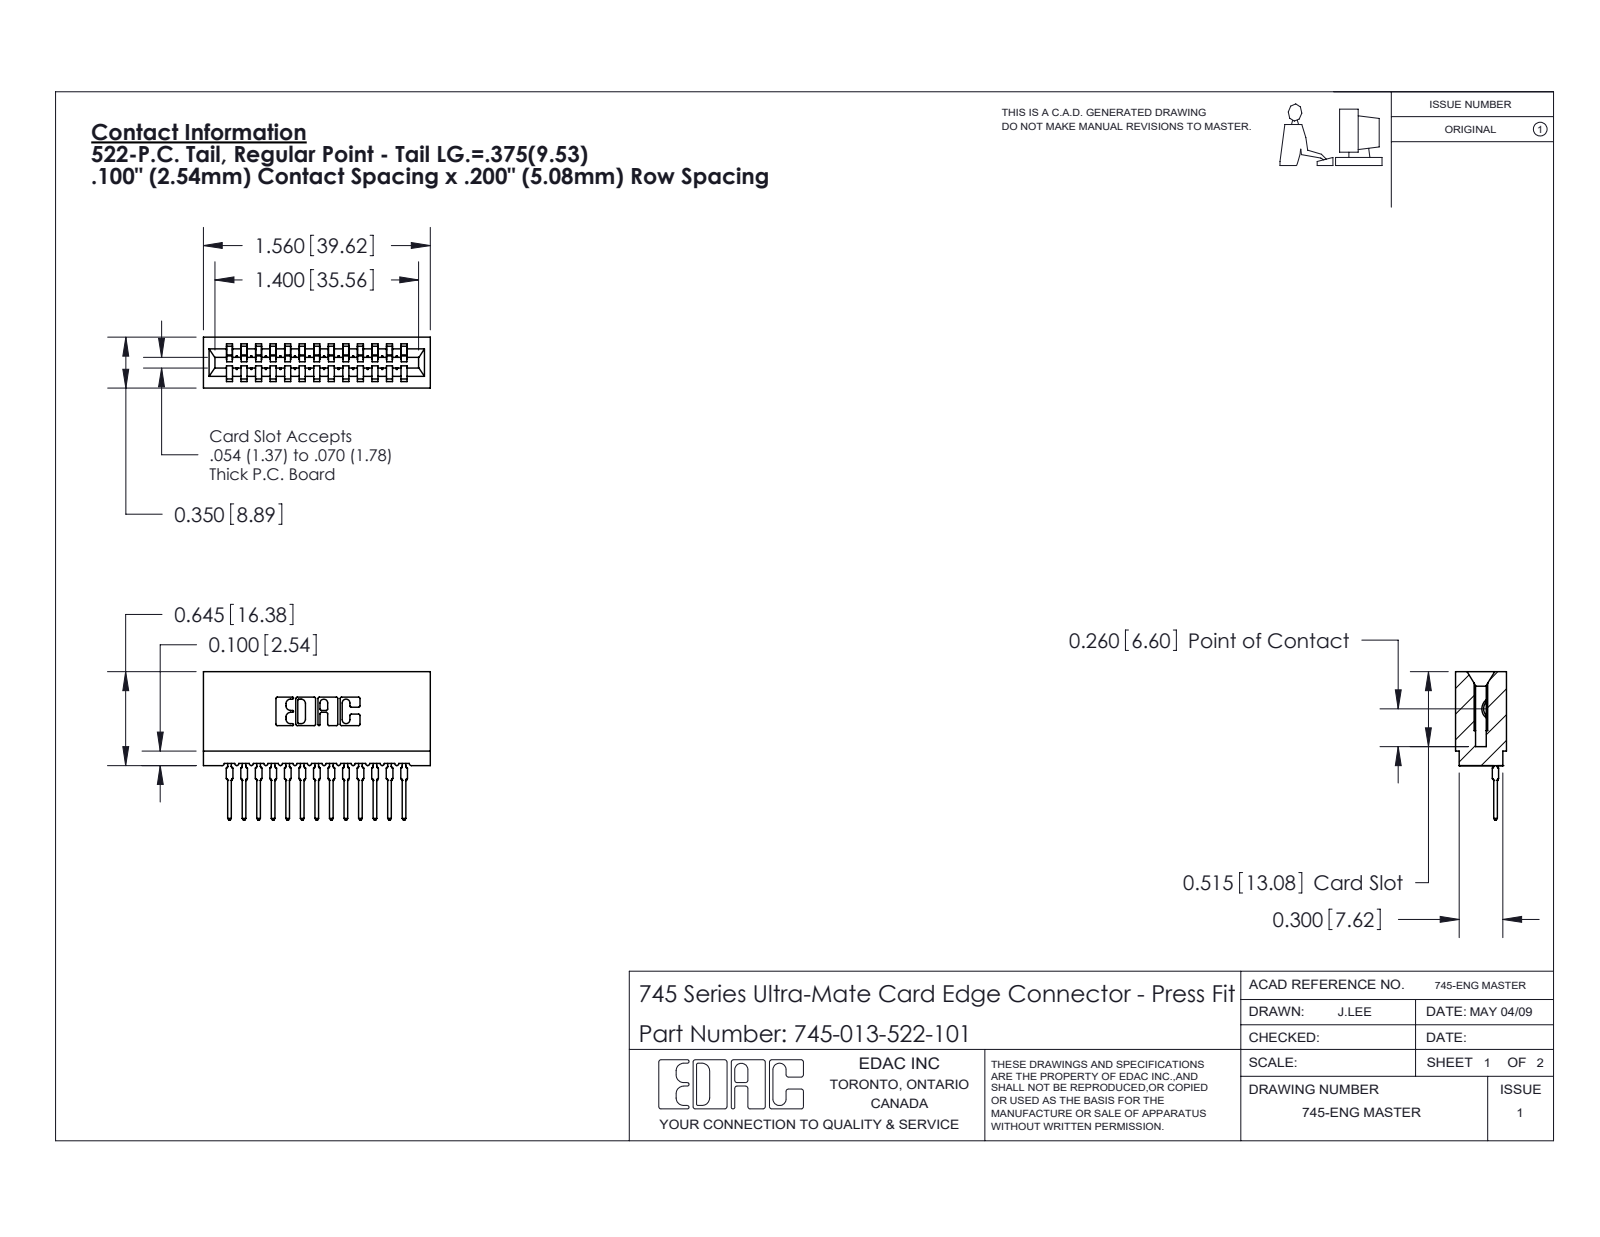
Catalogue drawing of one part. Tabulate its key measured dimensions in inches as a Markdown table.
| quantity | value |
| --- | --- |
| part name | 745-013-522-101; 745-292-001_522; 745 Part_Insulator Option - 01 |
| STEP written by | SolidWorks 2020 (CONFIG_CONTROL_DESIGN) |
| units | inches |
| bodies | 14 solids, 1551 faces (926 planar, 287 cylindrical, 338 other) |
| overall size | 1.56 × 1.021 × 0.35 |
| volume | 0.222 in³ |
| surface area | 9.65 in² |
| partial cylindrical surfaces (radius × count) | 0.015 × 26, 0.021 × 26, 0.01 × 22, 0.007 × 6, 0.031 × 6, 0.005 × 4, 0.011 × 4, 0.026 × 3 |
| main face-to-face distances | 0.1, 0.2, 0.3, 0.4, 0.5, 0.6, 0.35, 0.7, 0.8, 0.138 |
